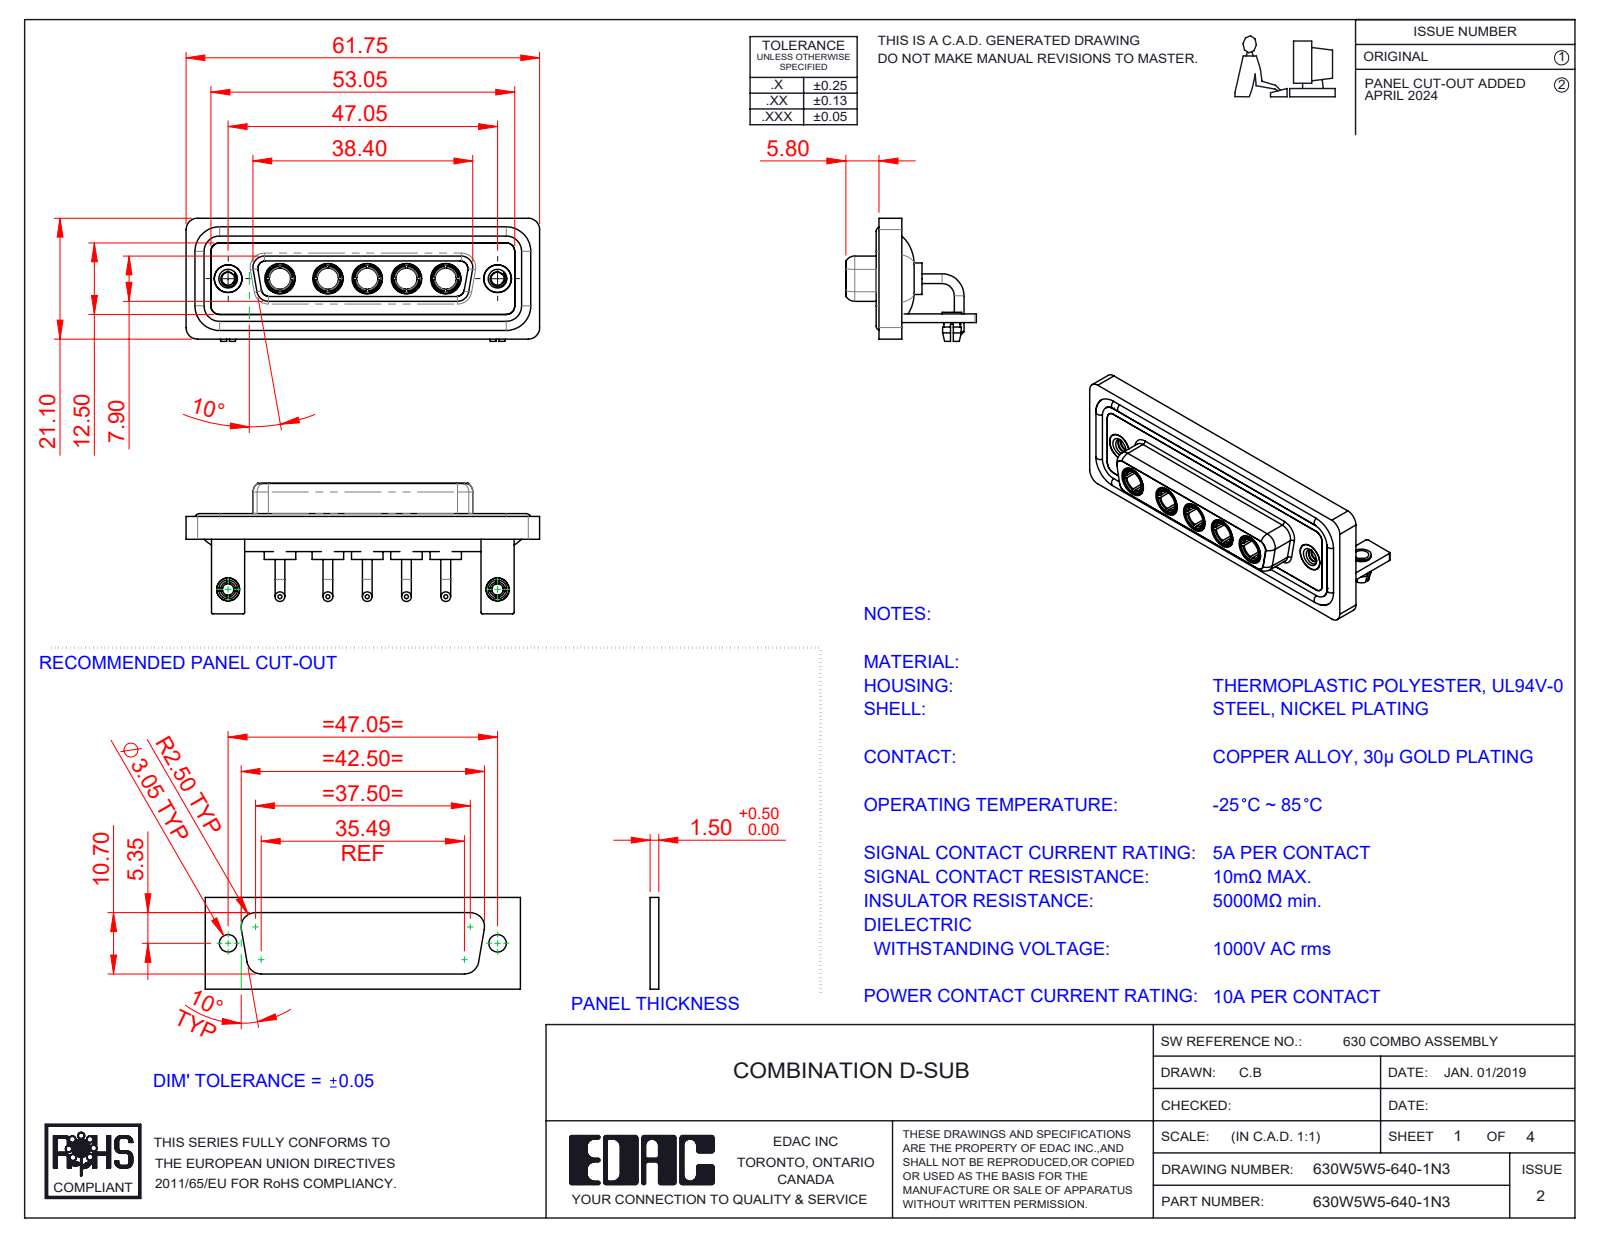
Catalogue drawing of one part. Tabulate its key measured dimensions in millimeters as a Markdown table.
| quantity | value |
| --- | --- |
| part name | 630Combo Waterproof Housing_25 Contacts; Power Socket_10A RA; 630Combo Shell Rear_25 Contacts; 630Combo Stabilizer Bracket_50 Contacts (+5 more) |
| STEP written by | SolidWorks 2023 (CONFIG_CONTROL_DESIGN) |
| units | millimeters |
| bodies | 21 solids, 916 faces (318 planar, 369 cylindrical, 229 other) |
| overall size | 61.75 × 22.8 × 21.5 |
| volume | 8 549 mm³ |
| surface area | 14 505 mm² |
| round holes (diameter × count) | 4.85 × 7, 3.7 × 5, 5.3 × 5, 2 × 2, 2.26 × 2, 2.5 × 2, 3.2 × 2, 4 × 2, 4.05 × 2, 5 × 2 |
| round bosses / shafts (diameter × count) | 1.7 × 10, 5.5 × 5, 5.2 × 5, 4.96 × 5, 4.75 × 5, 3.75 × 5, 1.6 × 4, 4.95 × 2 |
| partial cylindrical surfaces (radius × count) | 2 × 19, 1.5 × 18, 0.25 × 16, 1.35 × 8, 1.6 × 8, 0.5 × 5, 2.1 × 5, 0.6 × 4 |
| main face-to-face distances | 0.4, 1.8, 1.5, 2.9, 3.7, 4.1, 1.1, 1.4, 1.6, 2.5 |
| hole center spacings | 6.86, 9.04, 38.01, 47.05, 6.87, 8.38, 13.72, 13.73 |
